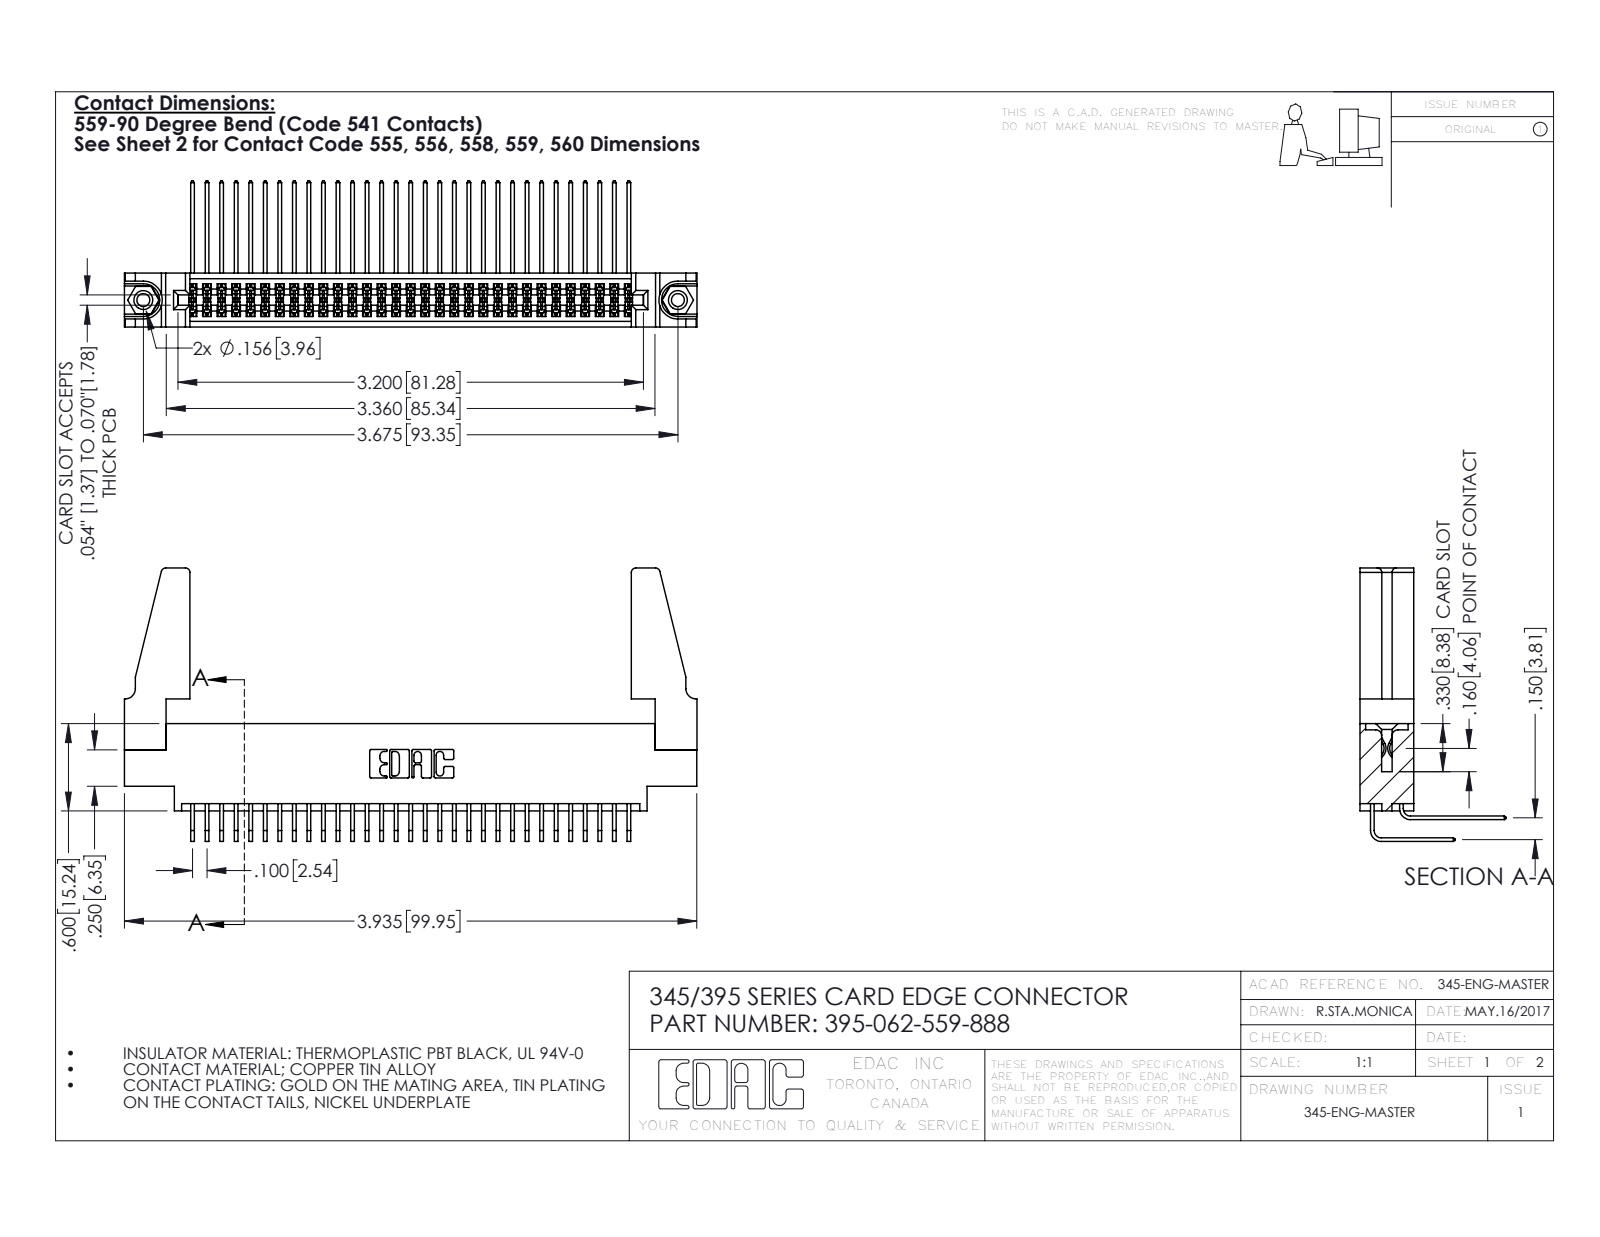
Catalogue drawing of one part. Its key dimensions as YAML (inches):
part_name: "345-292-001_559 Tail - 2; 345-220-078_345-220-088; 345-250-001_345-250-001-102; 395-062-559-888 (+2 more)"
step_written_by: "SolidWorks 2016 (CONFIG_CONTROL_DESIGN)"
units: inches
bodies: {solids: 67, faces: 3478, planar: 2326, cylindrical: 1136, other: 16}
overall_size: [3.936, 1.879, 1.005]
volume: 0.8
surface_area: 29.91
round_holes:
  - {diameter: 0.089, count: 2}
  - {diameter: 0.125, count: 2}
  - {diameter: 0.156, count: 2}
  - {diameter: 0.064, count: 1}
round_bosses_or_shafts:
  - {diameter: 0.155, count: 2}
partial_cylinders:
  - {radius: 0.006, count: 93}
  - {radius: 0.01, count: 22}
  - {radius: 0.03, count: 8}
  - {radius: 0.007, count: 6}
  - {radius: 0.031, count: 6}
  - {radius: 0.026, count: 3}
  - {radius: 0.014, count: 2}
  - {radius: 0.019, count: 2}
face_to_face_distances: [0.072, 0.298, 0.37, 0.2, 0.098, 0.272, 0.025, 0.225, 0.15, 0.175]
hole_center_spacings: [0.27, 3.44, 3.675]
